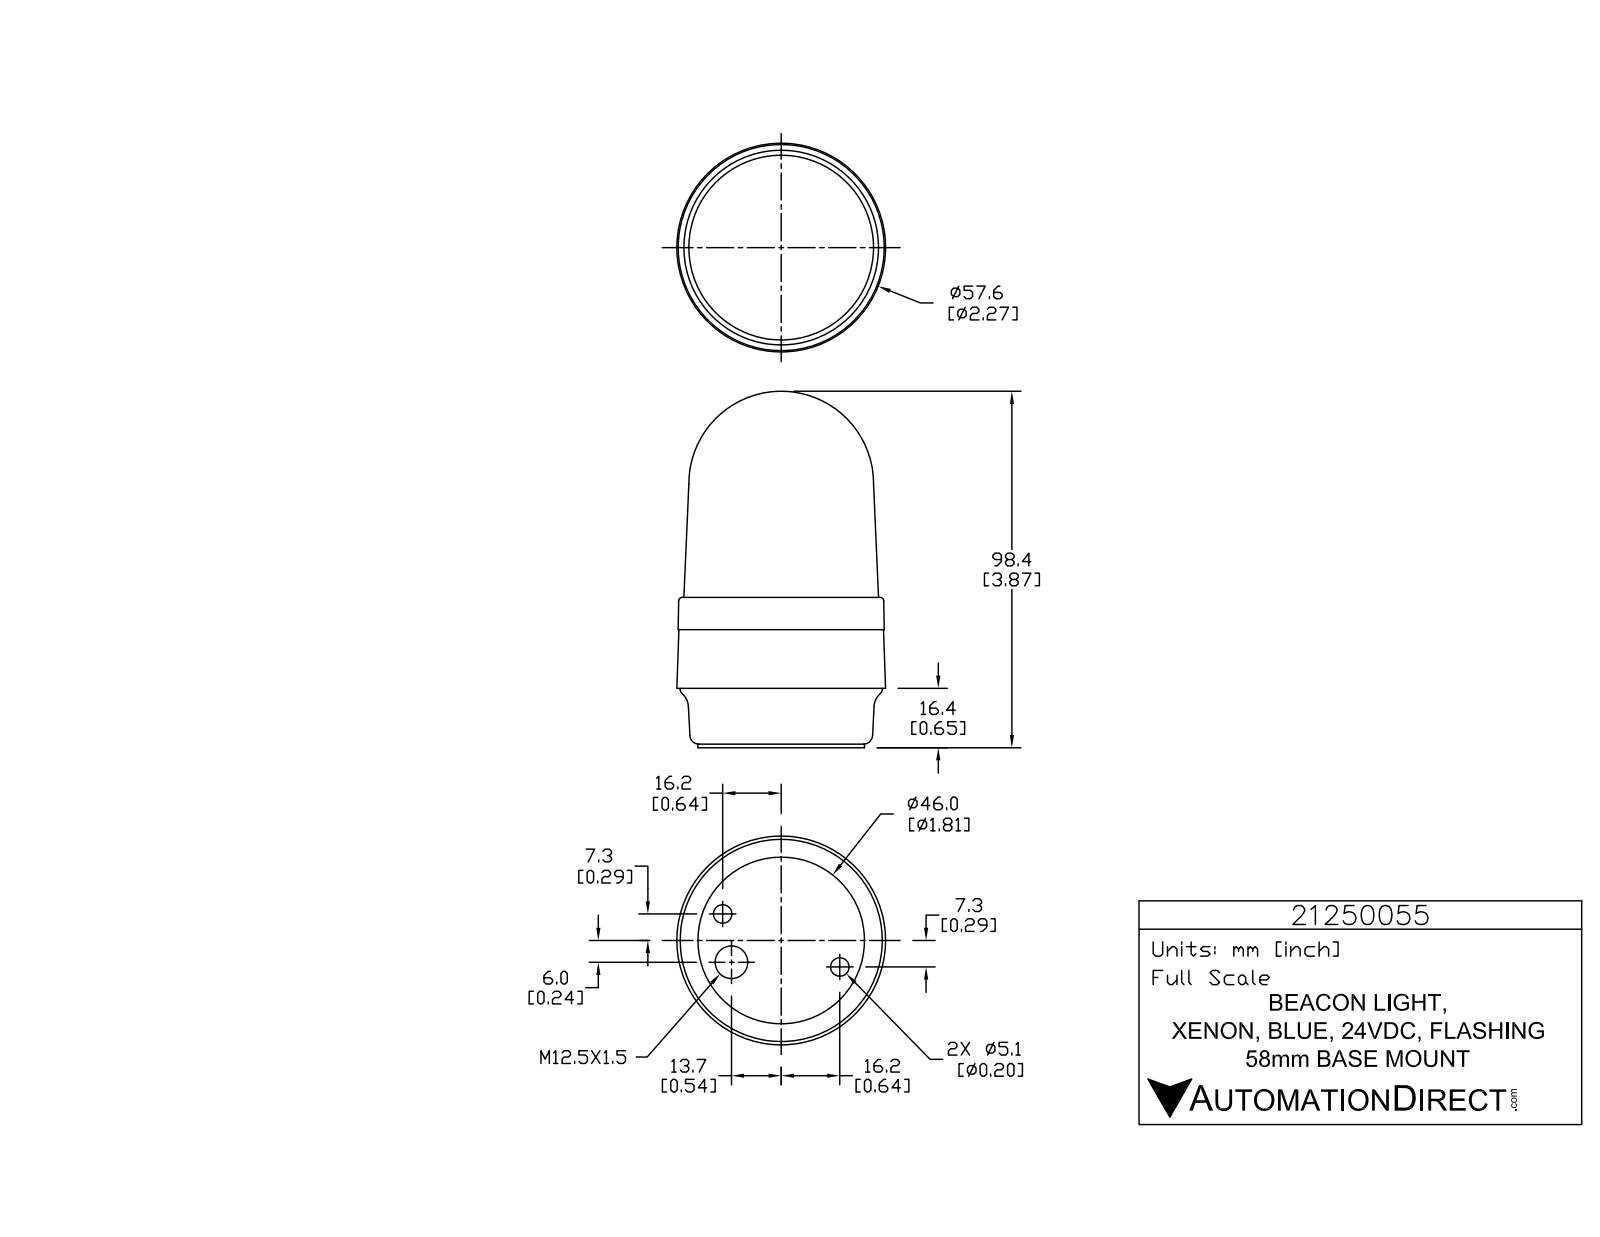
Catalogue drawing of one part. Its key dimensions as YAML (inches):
part_name: "21250055"
step_written_by: "SolidWorks 2015 (AUTOMOTIVE_DESIGN)"
units: inches
bodies: {solids: 1, faces: 764, planar: 527, cylindrical: 145, other: 92}
overall_size: [3.874, 2.269, 2.269]
volume: 12.2
surface_area: 29.33
round_holes:
  - {diameter: 0.039, count: 3}
  - {diameter: 0.201, count: 2}
  - {diameter: 0.354, count: 1}
round_bosses_or_shafts:
  - {diameter: 0.226, count: 3}
  - {diameter: 0.056, count: 3}
  - {diameter: 2.197, count: 1}
  - {diameter: 1.811, count: 1}
partial_cylinders:
  - {radius: 0.008, count: 6}
  - {radius: 0.008, count: 6}
  - {radius: 0.008, count: 6}
  - {radius: 0.131, count: 6}
  - {radius: 0.004, count: 3}
  - {radius: 0.005, count: 3}
  - {radius: 0.007, count: 3}
  - {radius: 0.008, count: 3}
face_to_face_distances: [0.646, 0.039, 0.606, 1.634, 1.594, 0.988, 1.283, 1.244, 0.638, 0.35]
hole_center_spacings: [0.534, 1.179, 1.398]
